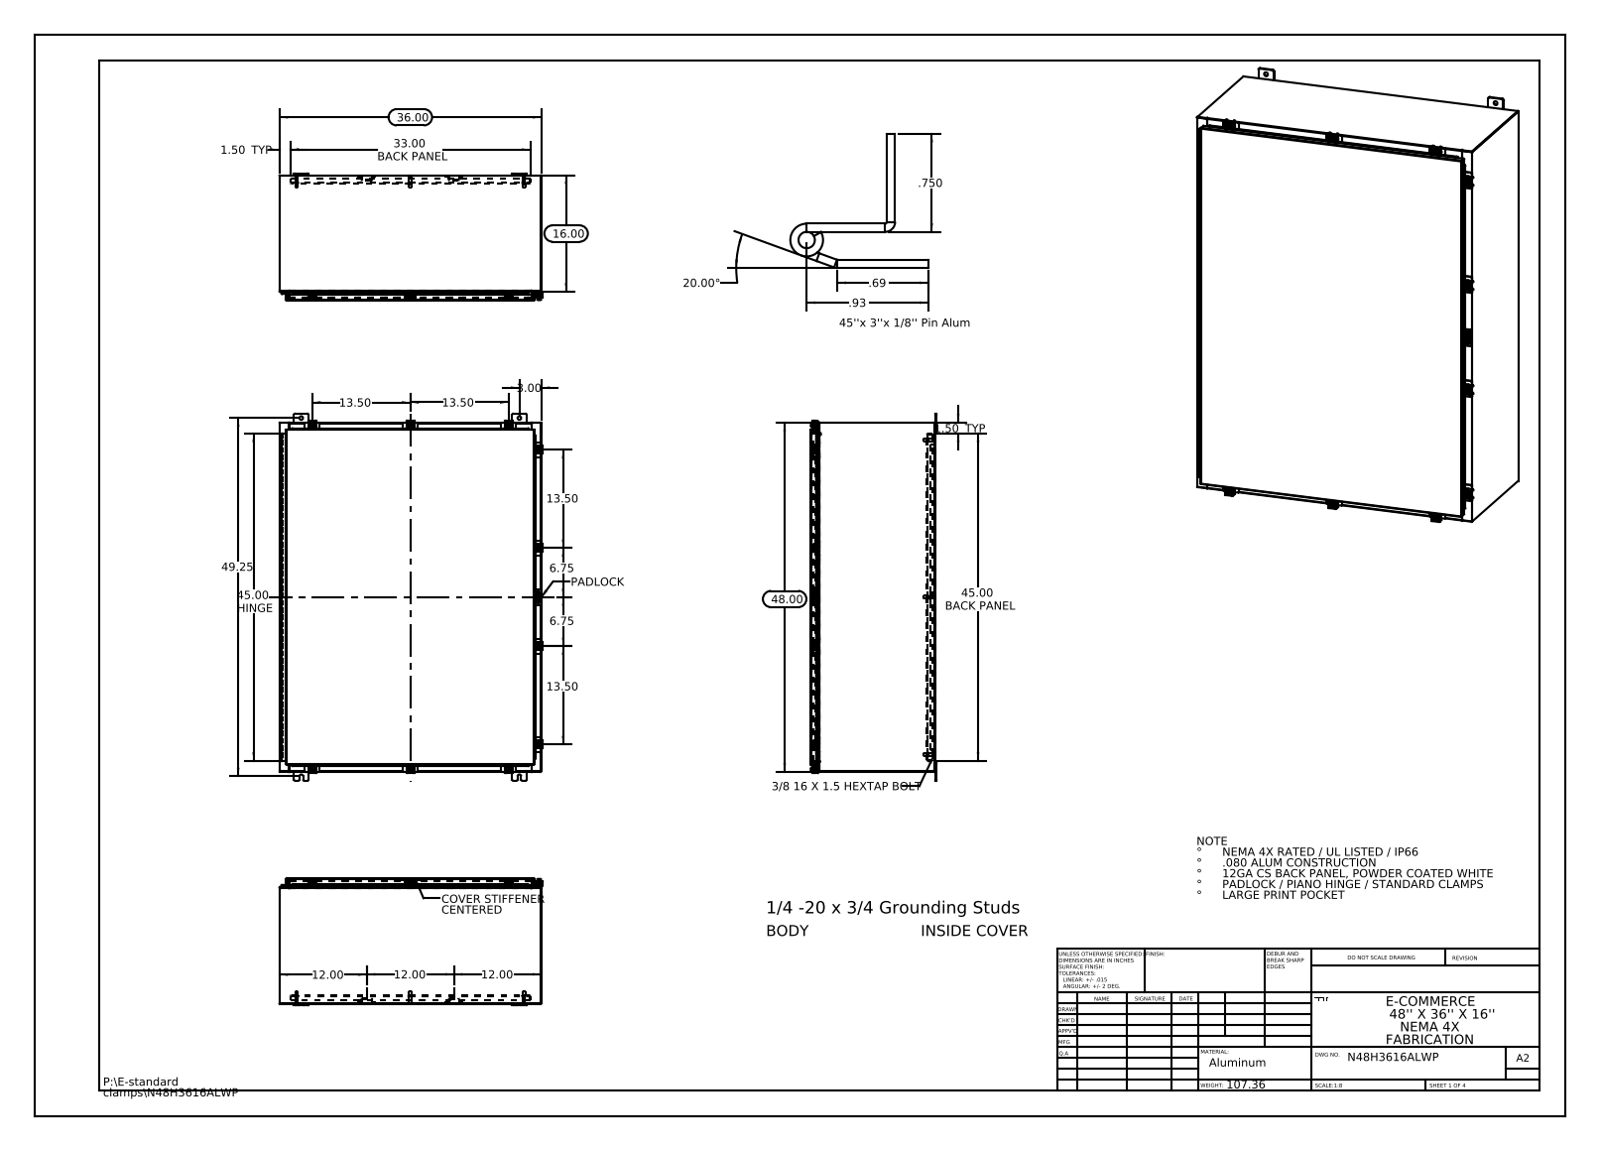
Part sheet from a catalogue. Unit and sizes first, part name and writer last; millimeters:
Units: millimetres
Overall size (bounding box): 1282.7 × 919.8 × 441.7
Round holes (diameter × count): ⌀12.7 ×12, ⌀5.4 ×10, ⌀6.6 ×10, ⌀6.4 ×6, ⌀3.2 ×2, ⌀3.2 ×1
Round bosses / shafts (diameter × count): ⌀6.4 ×11, ⌀12.7 ×10, ⌀10.1 ×10, ⌀15.9 ×8, ⌀9.5 ×8, ⌀8.4 ×8
Partial cylindrical surfaces — rounded edges, fillets, slot ends (radius × count): R1.5 ×46, R0.3 ×39, R2.2 ×33, R4.8 ×24, R3 ×20, R3.6 ×20, R1.3 ×15, R2 ×14
Main face-to-face distances: 1.9, 435, 433.1, 2.6, 436.9, 912.5, 25.4, 409.6, 27.3, 407.7
Hole centre spacings: 342.9, 347, 508, 511.1, 549.3, 605, 685.8, 965.3
Volume: 11 480 000 mm³ · Surface area: 11 350 000 mm²
Bodies: 74 solids, 2999 faces (1562 planar, 1269 cylindrical, 168 other)
Part name (STEP PRODUCT): N48H3616ALWP Bottom; N48H3616ALWP Padlock Hasp; N48H3616ALWP; N48H3616ALWP Door Stiffener (+8 more)
STEP written by: SolidWorks 2013 (CONFIG_CONTROL_DESIGN)
